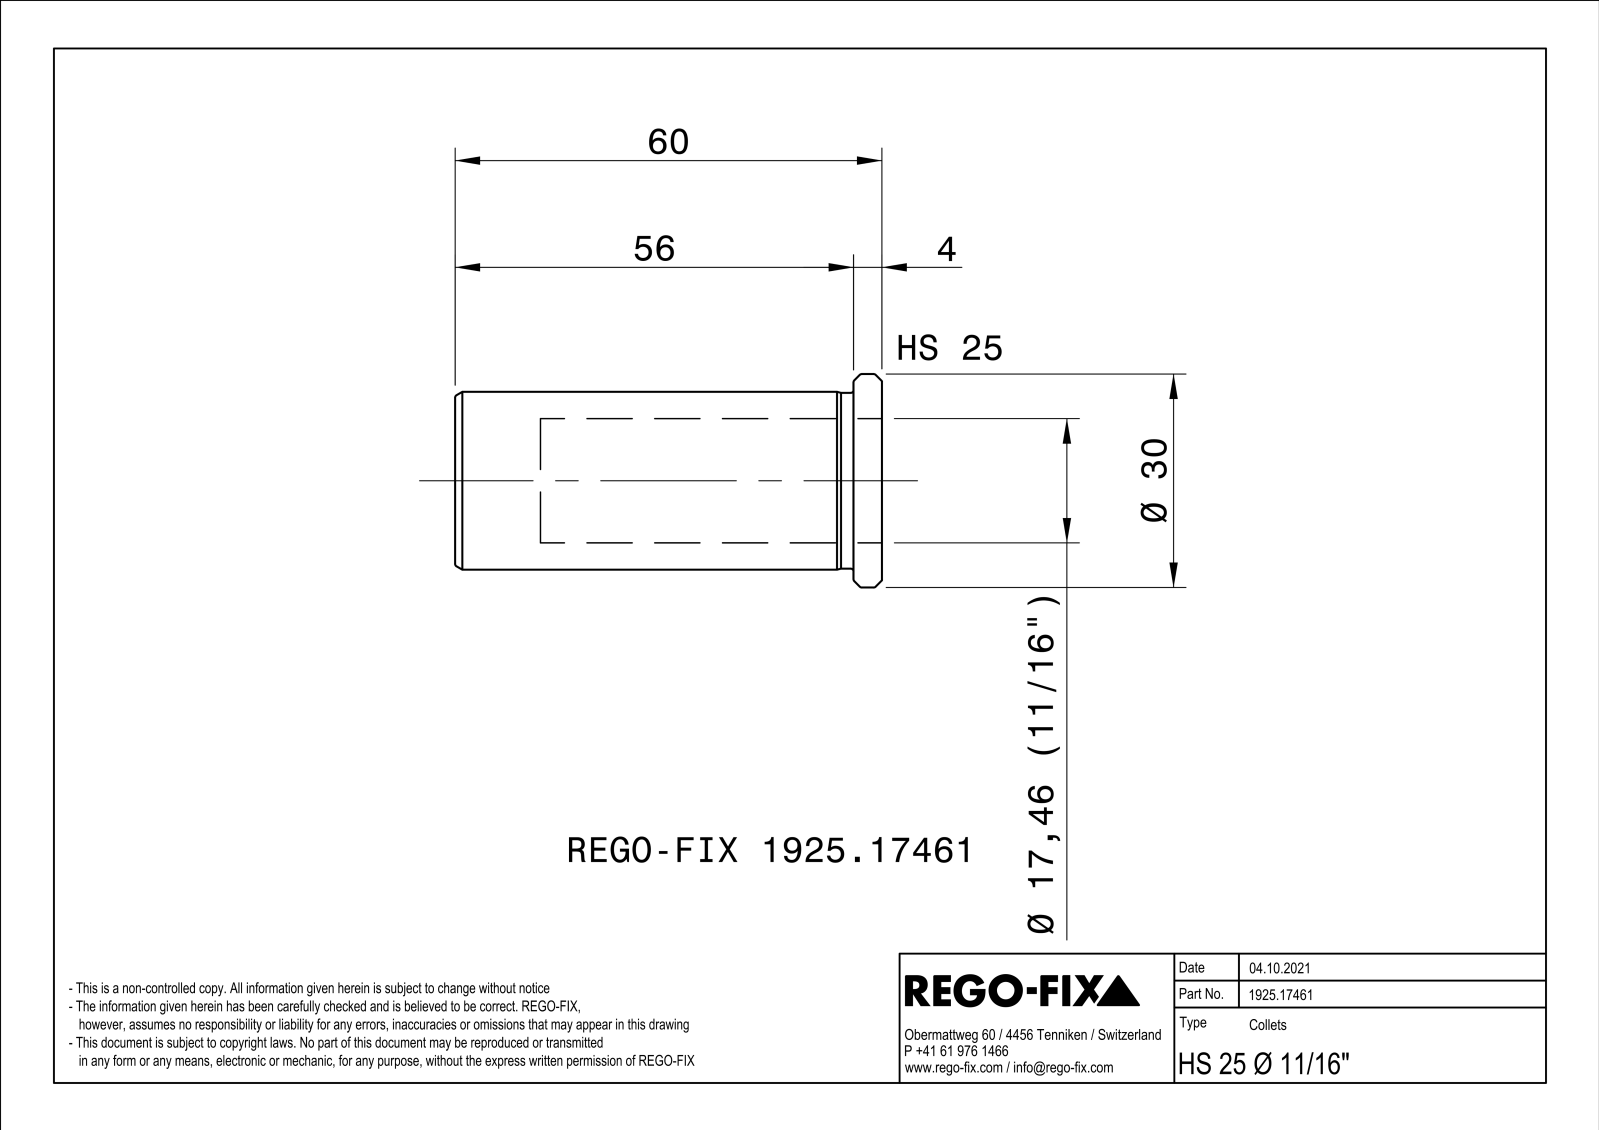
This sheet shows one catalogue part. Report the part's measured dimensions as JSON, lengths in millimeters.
{"part_name": "NOCUT", "step_written_by": "SIEMENS PLM Software Solid Edge ST10 (AUTOMOTIVE_DESIGN)", "units": "millimeters", "bodies": {"solids": 1, "faces": 71, "planar": 22, "cylindrical": 11, "other": 38}, "overall_size": [60, 29.98, 29.98], "volume_mm3": 14266, "surface_area_mm2": 9730, "round_holes": [[17.46, 1], [20.5, 1]], "round_bosses_or_shafts": [[30, 1], [25, 1], [24.7, 1]], "face_to_face_distances": [1, 4, 60, 56]}
